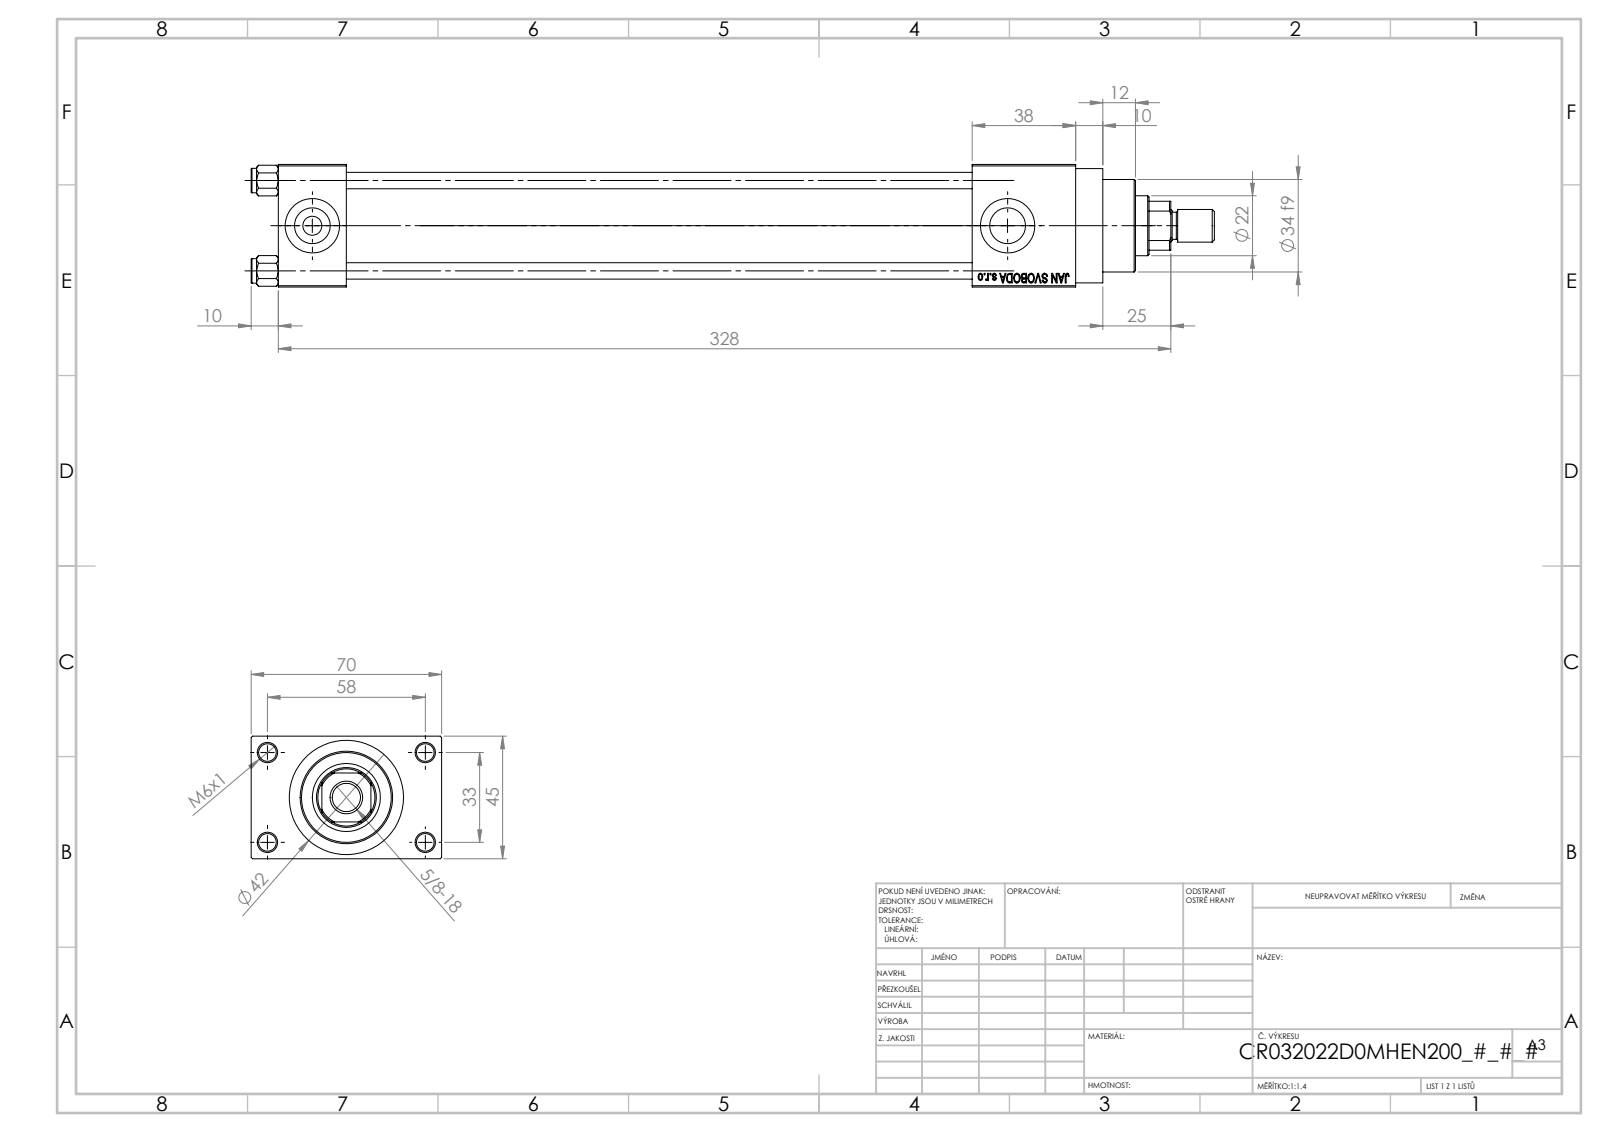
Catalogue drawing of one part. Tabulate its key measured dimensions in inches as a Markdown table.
| quantity | value |
| --- | --- |
| part name | V215_VC_A; NUT_M5_D; V215CR_D_Body; ROD_END_E (+2 more) |
| STEP written by | SolidWorks 2019 (CONFIG_CONTROL_DESIGN) |
| units | inches |
| bodies | 12 solids, 1116 faces (500 planar, 92 cylindrical, 524 other) |
| overall size | 13.937 × 2.756 × 1.772 |
| volume | 23.98 in³ |
| surface area | 226.9 in² |
| round holes (diameter × count) | 0.236 × 4, 0.256 × 4, 0.276 × 2, 0.518 × 2, 0.787 × 2, 0.413 × 1, 0.866 × 1, 0.945 × 1, 0.984 × 1, 1.26 × 1, 1.299 × 1 |
| round bosses / shafts (diameter × count) | 0.354 × 4, 1.654 × 1, 1.496 × 1, 1.339 × 1, 0.472 × 1, 0.394 × 1 |
| partial cylindrical surfaces (radius × count) | 0.413 × 1 |
| main face-to-face distances | 1.772, 0.984, 0.492, 9.055, 10.039, 2.264, 10.551, 1.496, 11.535, 2.756 |
| hole center spacings | 0.488, 0.924, 1.307, 1.314, 1.392, 1.795, 2.219, 1.299 |
